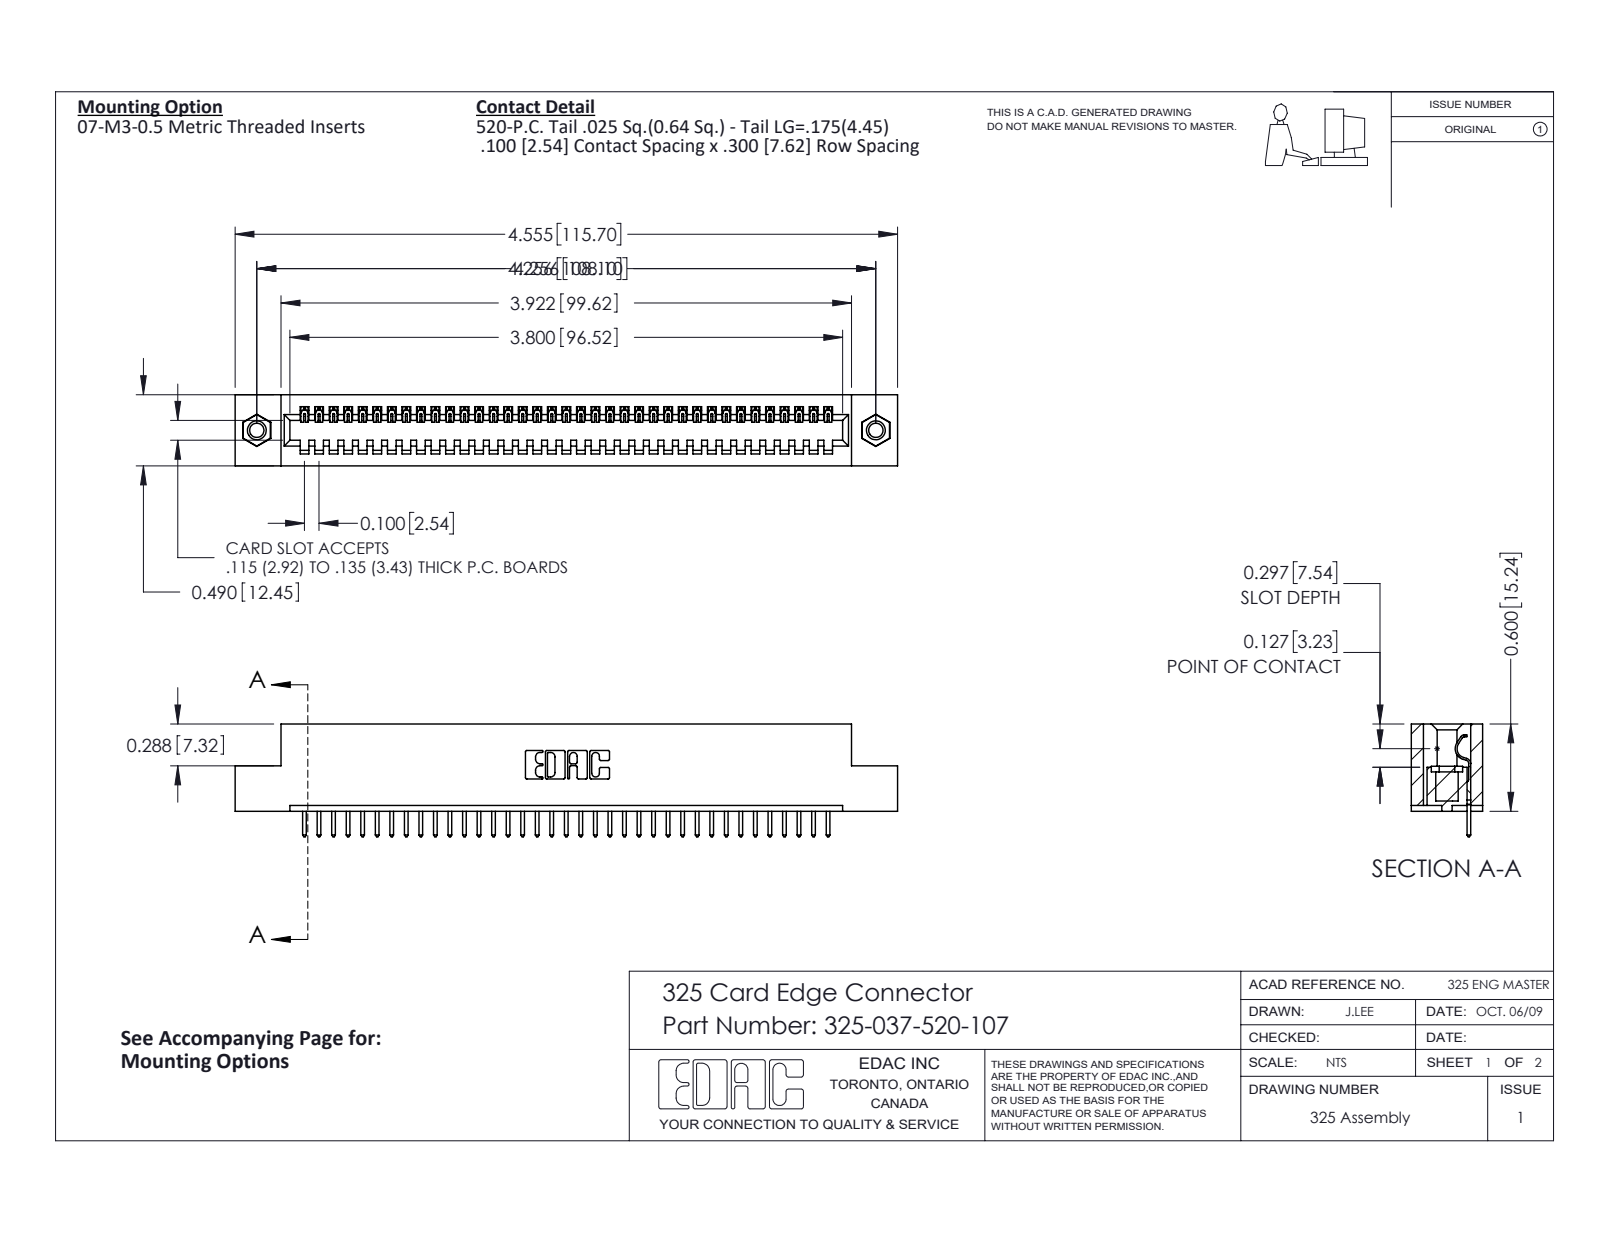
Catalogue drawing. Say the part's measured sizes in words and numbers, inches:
The part is named "345-250-001_345-250-005-103; 325-292-001_325-293-120; 325-037-520-107; 325 Part_TI". Its 3-D file was written by "SolidWorks 2016 (CONFIG_CONTROL_DESIGN)". It is 40 solids with 2320 faces: 1656 planar, 648 cylindrical and 16 other. Overall it measures 4.555 by 0.775 by 0.49 inches. Its volume is 0.887 cubic inches and its surface area 23.93 square inches. Round holes: 2 of diameter 0.098, 2 of diameter 0.125, 2 of diameter 0.16. Round bosses or shafts: 2 of diameter 0.155. Partial cylindrical surfaces (rounded edges, fillets, slot ends): 74 of radius 0.006, 74 of radius 0.01, 22 of radius 0.01, 6 of radius 0.007, 6 of radius 0.031, 3 of radius 0.026, 1 of radius 0.014, 1 of radius 0.022. The main face-to-face distances are 0.083, 0.407, 0.49, 0.3, 0.107, 0.383, 0.025, 0.325, 0.56, 0.263. The hole center spacings are 4.256.
